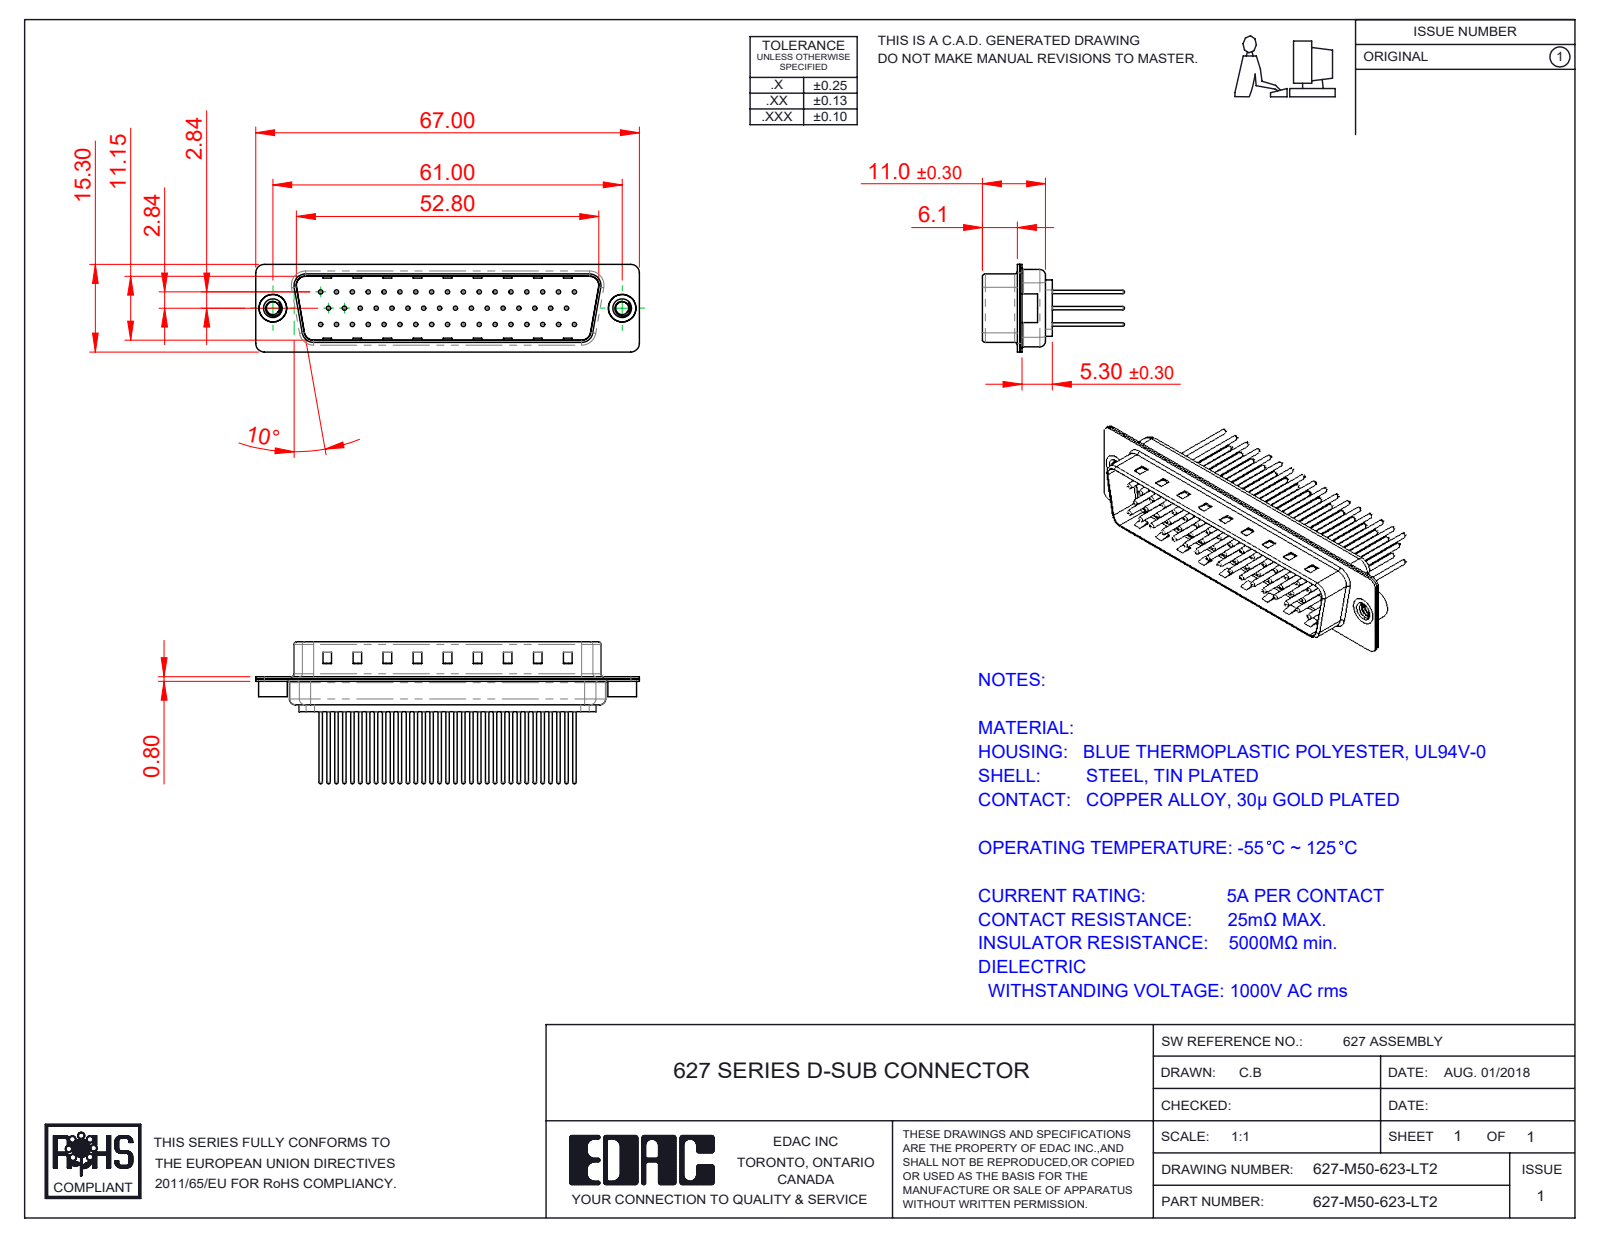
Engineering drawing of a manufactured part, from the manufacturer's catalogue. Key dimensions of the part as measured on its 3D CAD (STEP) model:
Part name (STEP PRODUCT): 627M Shell Rear_50 Contacts; 627M Contact Row 1_23; 627M 4-40 Threaded Rivet; 627M Contact Row 3_23 (+4 more)
STEP written by: SolidWorks 2020 (CONFIG_CONTROL_DESIGN)
Units: millimetres
Bodies: 55 solids, 2262 faces (553 planar, 841 cylindrical, 868 other)
Overall size (bounding box): 67 × 24.77 × 15.3
Volume: 4 622 mm³ · Surface area: 11 347 mm²
Round holes (diameter × count): ⌀0.75 ×50, ⌀1.6 ×50, ⌀2 ×50, ⌀2.26 ×2, ⌀4 ×2, ⌀4.8 ×2
Round bosses / shafts (diameter × count): ⌀1.5 ×50, ⌀0.6 ×50, ⌀5 ×2, ⌀4.9 ×2
Partial cylindrical surfaces — rounded edges, fillets, slot ends (radius × count): R1.5 ×16, R2 ×12, R0.5 ×8, R1.6 ×8, R0.25 ×4, R0.6 ×4, R0.65 ×4, R0.9 ×4
Main face-to-face distances: 0.4, 11.55, 5.7, 6.1, 0.78, 0.77, 12.33, 12.32, 13.1, 5.3
Hole centre spacings: 3.16, 2.77, 5.54, 8.31, 11.08, 13.85, 16.62, 5.03
